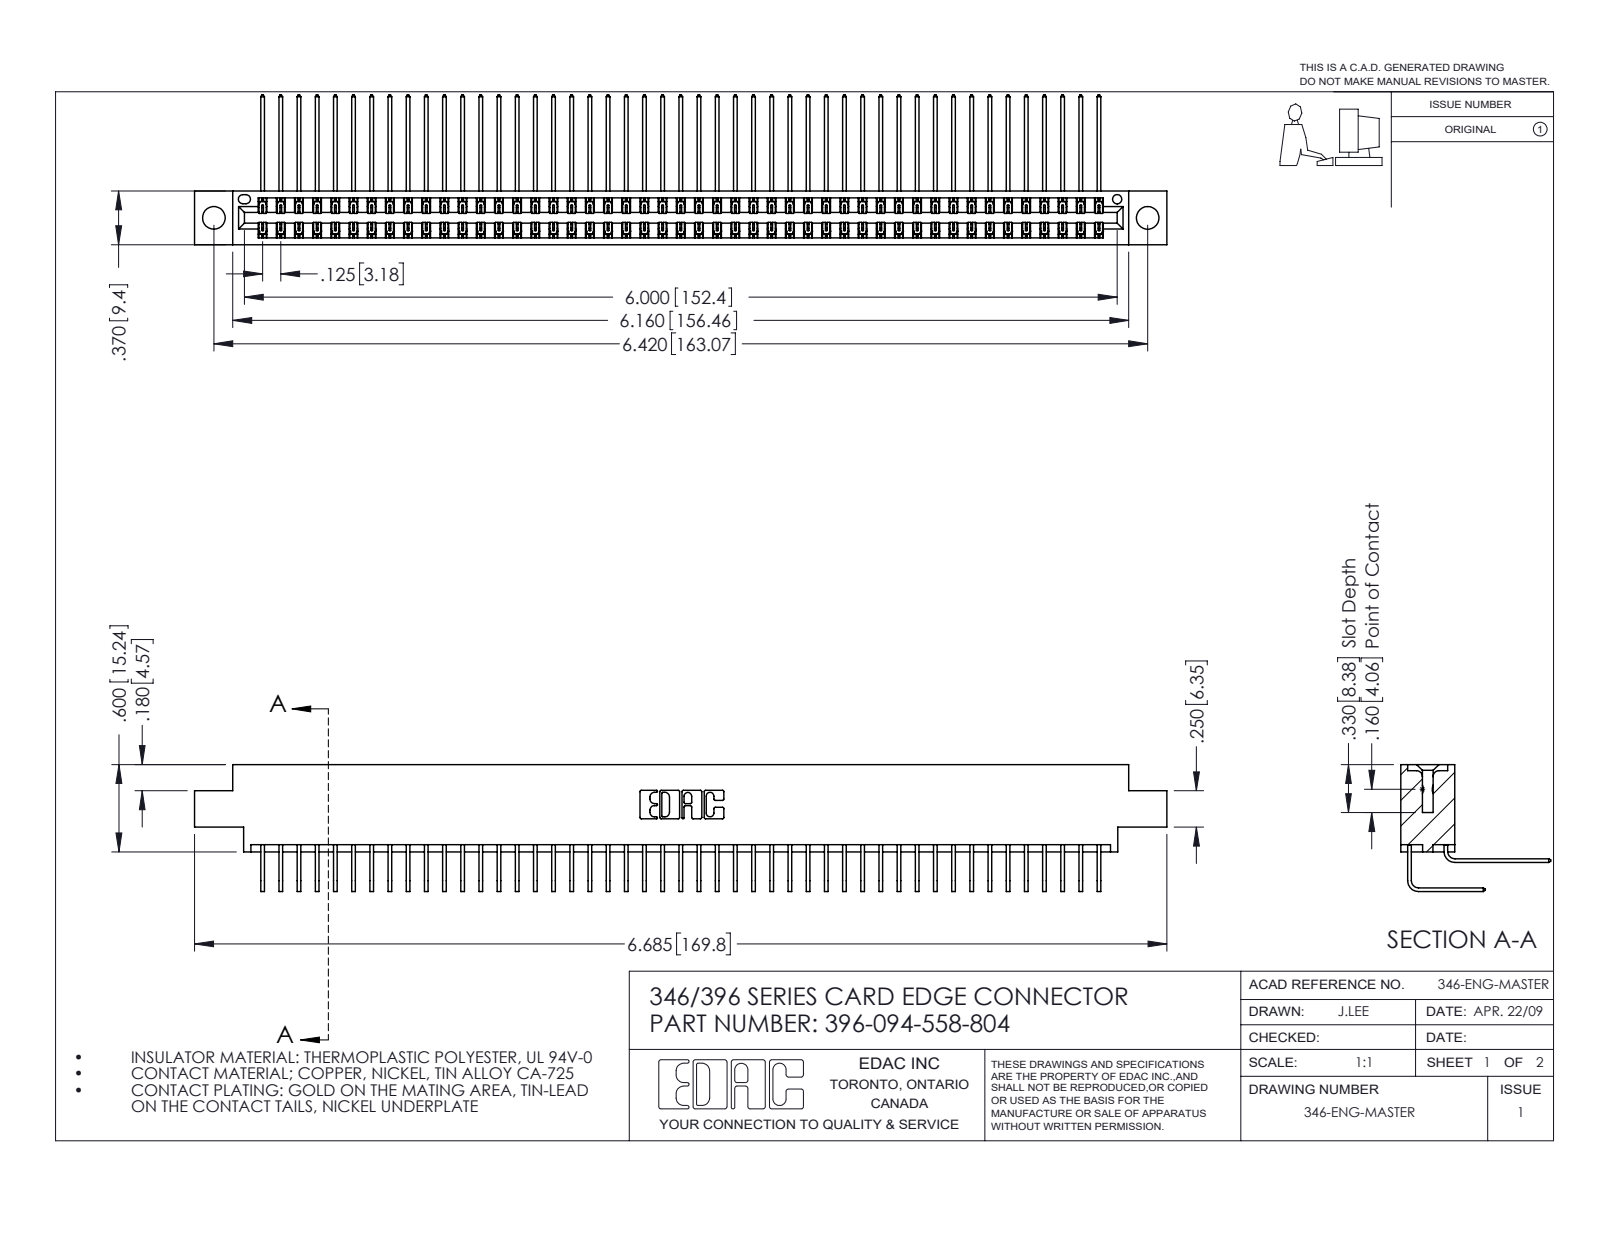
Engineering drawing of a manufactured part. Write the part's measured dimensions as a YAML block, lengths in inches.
part_name: "345-292-001_558 Tail - 2; 345-292-001_558 559 Tail - 1; 346 Part_0.170 Offset - 0.156 Dia-TH; 396-094-558-804"
step_written_by: "SolidWorks 2016 (CONFIG_CONTROL_DESIGN)"
units: inches
bodies: {solids: 95, faces: 5202, planar: 3558, cylindrical: 1644, other: 0}
overall_size: [6.685, 1.03, 0.873]
volume: 1.031
surface_area: 40.14
round_holes:
  - {diameter: 0.156, count: 2}
  - {diameter: 0.064, count: 1}
partial_cylinders:
  - {radius: 0.006, count: 141}
  - {radius: 0.01, count: 22}
  - {radius: 0.007, count: 6}
  - {radius: 0.031, count: 6}
  - {radius: 0.026, count: 3}
  - {radius: 0.014, count: 2}
  - {radius: 0.022, count: 2}
  - {radius: 0.024, count: 2}
face_to_face_distances: [0.322, 0.048, 0.025, 0.37, 0.25, 0.298, 0.072, 0.275, 0.148, 0.222]
hole_center_spacings: [0.246, 6.211, 6.42]
